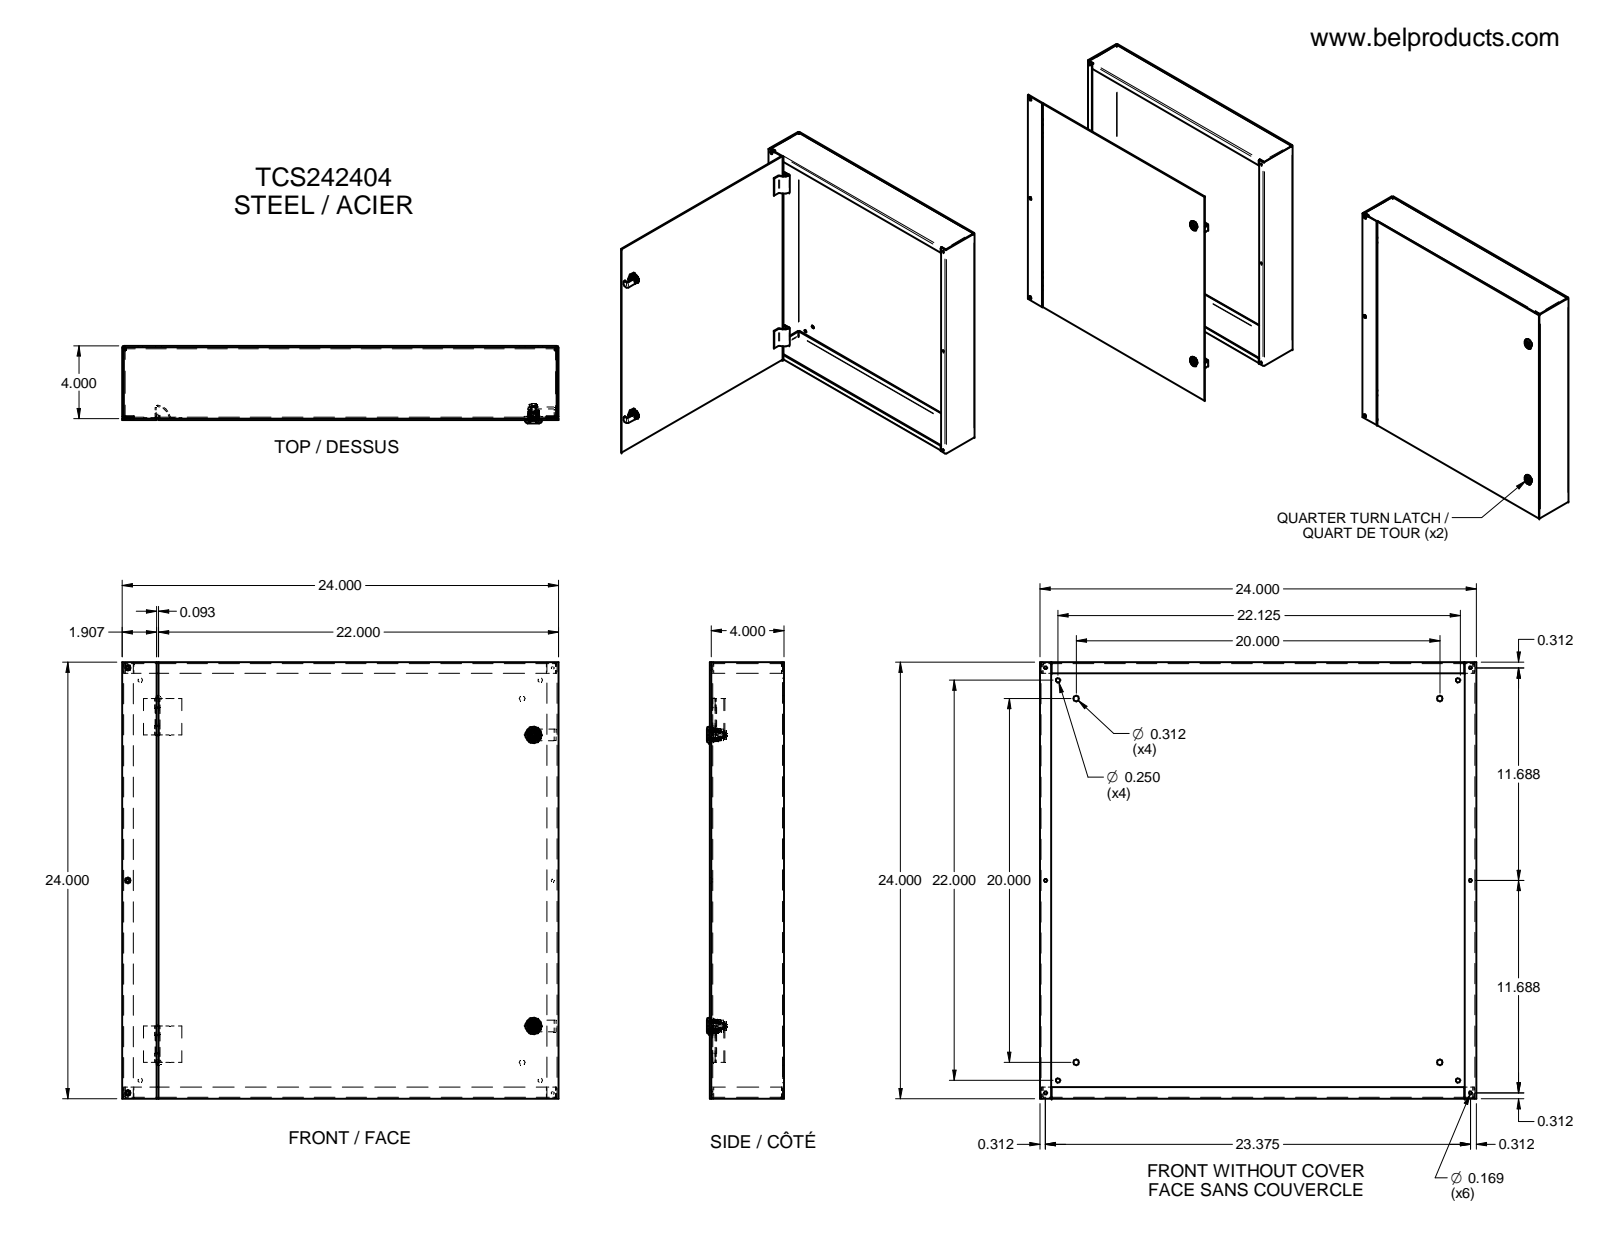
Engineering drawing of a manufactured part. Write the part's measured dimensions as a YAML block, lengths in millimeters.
part_name: "LOCK AVEC TOURNEVIS TYPE 4-12 SANS CAME; HOSING-oa0; INSERT POUR TOURNEVIS-oa1; NOIX DE FIXATION-oa2 (+8 more)"
step_written_by: "Unknown (AUTOMOTIVE_DESIGN)"
units: millimeters
bodies: {solids: 27, faces: 1077, planar: 536, cylindrical: 261, other: 280}
overall_size: [609.6, 609.6, 107.97]
volume: 2000000
surface_area: 2125000
round_holes:
  - {diameter: 7.92, count: 7}
  - {diameter: 4.29, count: 6}
  - {diameter: 6.35, count: 4}
  - {diameter: 6.99, count: 2}
  - {diameter: 9.1, count: 2}
  - {diameter: 11.18, count: 2}
  - {diameter: 12.83, count: 2}
  - {diameter: 15.8, count: 2}
  - {diameter: 17.46, count: 2}
  - {diameter: 3.81, count: 1}
round_bosses_or_shafts:
  - {diameter: 22.86, count: 2}
  - {diameter: 22.61, count: 2}
  - {diameter: 15.75, count: 2}
  - {diameter: 12.95, count: 2}
  - {diameter: 12.62, count: 2}
  - {diameter: 12.19, count: 2}
  - {diameter: 11.86, count: 2}
  - {diameter: 10.08, count: 2}
partial_cylinders:
  - {radius: 9.53, count: 22}
  - {radius: 0.25, count: 16}
  - {radius: 0.81, count: 13}
  - {radius: 2.72, count: 12}
  - {radius: 9.42, count: 4}
  - {radius: 1.52, count: 2}
  - {radius: 3.05, count: 2}
  - {radius: 6.22, count: 2}
face_to_face_distances: [1.91, 101.6, 99.69, 103.51, 1.9, 609.6, 607.69, 607.7, 605.78, 605.8]
hole_center_spacings: [534, 552.52, 576.52, 593.72, 24.69, 35.92, 60.61, 257.59]
